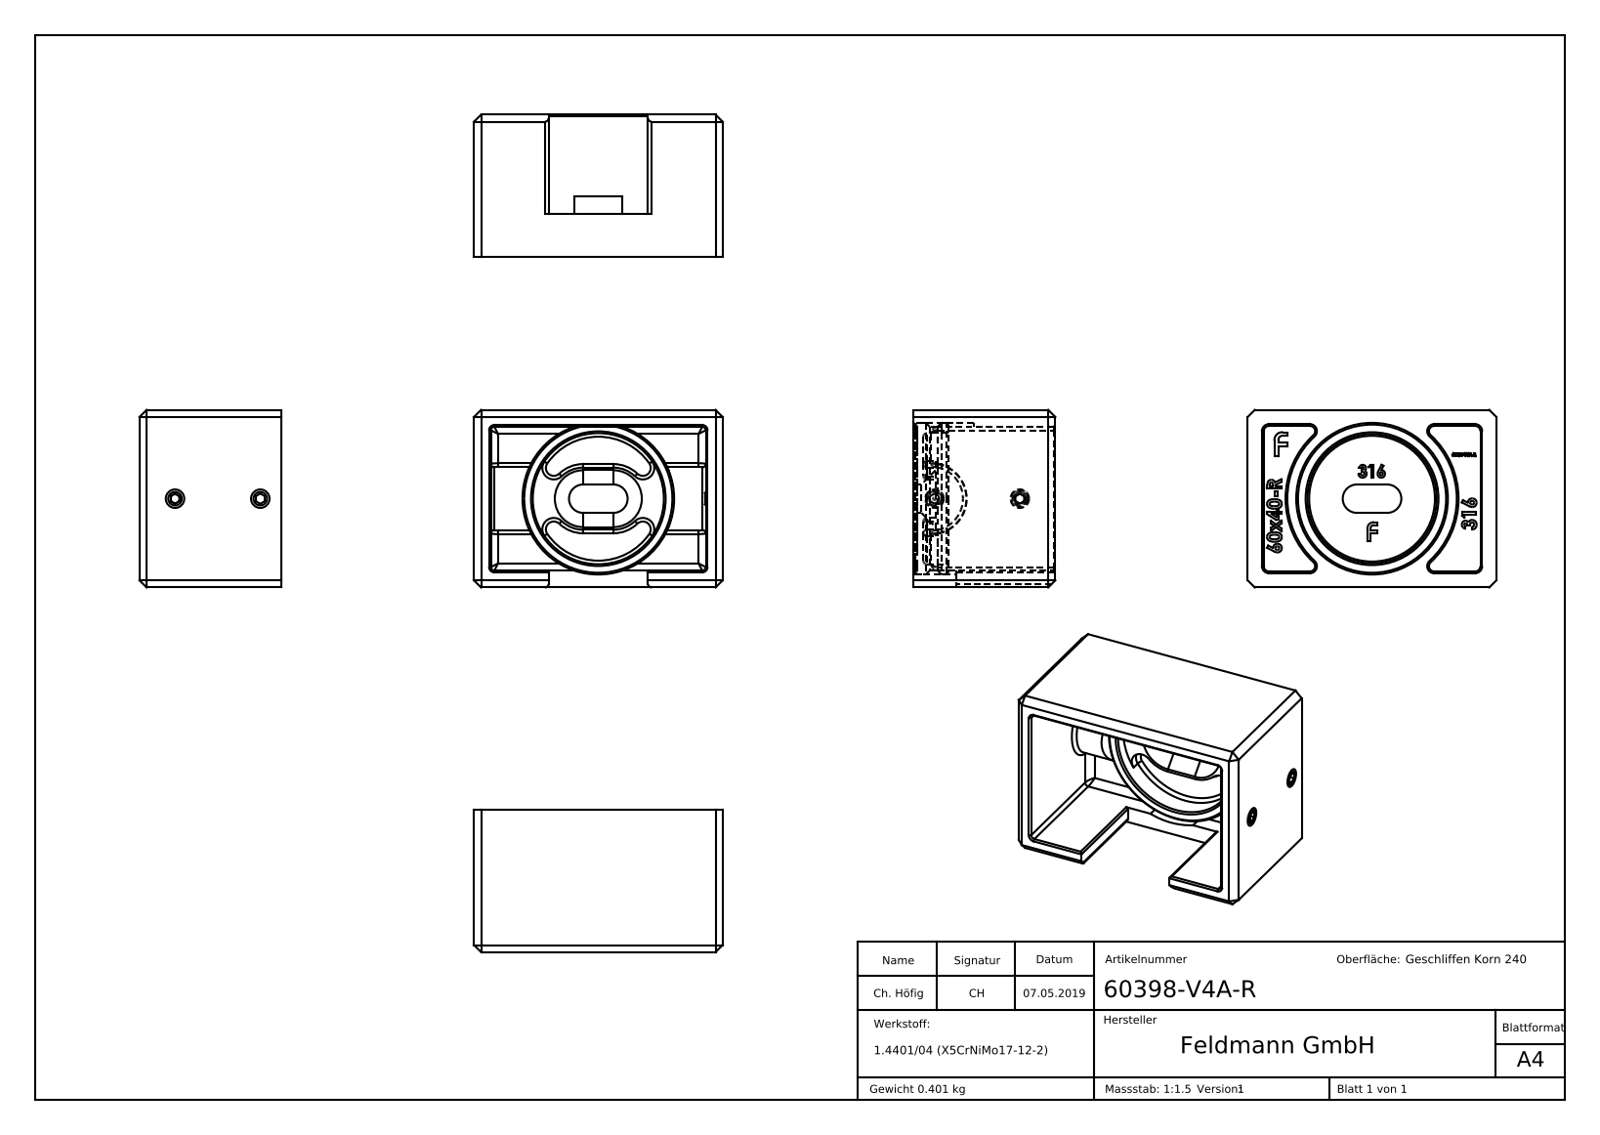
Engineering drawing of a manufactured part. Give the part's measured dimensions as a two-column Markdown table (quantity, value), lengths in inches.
| quantity | value |
| --- | --- |
| part name | DIN914_DIN 914 M5x15; 60398-V4A-R; 6039X-240-X Teil2_6039X-V4A-X Teil2; DIN913_DIN 913 M5x5 (+1 more) |
| STEP written by | SolidWorks 2015 (CONFIG_CONTROL_DESIGN) |
| units | inches |
| bodies | 4 solids, 553 faces (268 planar, 74 cylindrical, 211 other) |
| overall size | 2.756 × 1.969 × 1.575 |
| volume | 3.056 in³ |
| surface area | 39.54 in² |
| round holes (diameter × count) | 0.165 × 2, 1.453 × 1 |
| round bosses / shafts (diameter × count) | 0.197 × 2, 1.681 × 1, 1.592 × 1 |
| partial cylindrical surfaces (radius × count) | 0.079 × 12, 0.039 × 10, 0.02 × 6, 0.127 × 4, 0.157 × 2, 0.344 × 2, 0.354 × 1, 0.939 × 1 |
| main face-to-face distances | 0.187, 1.781, 2.569, 1.969, 2.756, 0.039, 2.382, 1.594, 0.197, 0.157 |
| hole center spacings | 0.945 |
